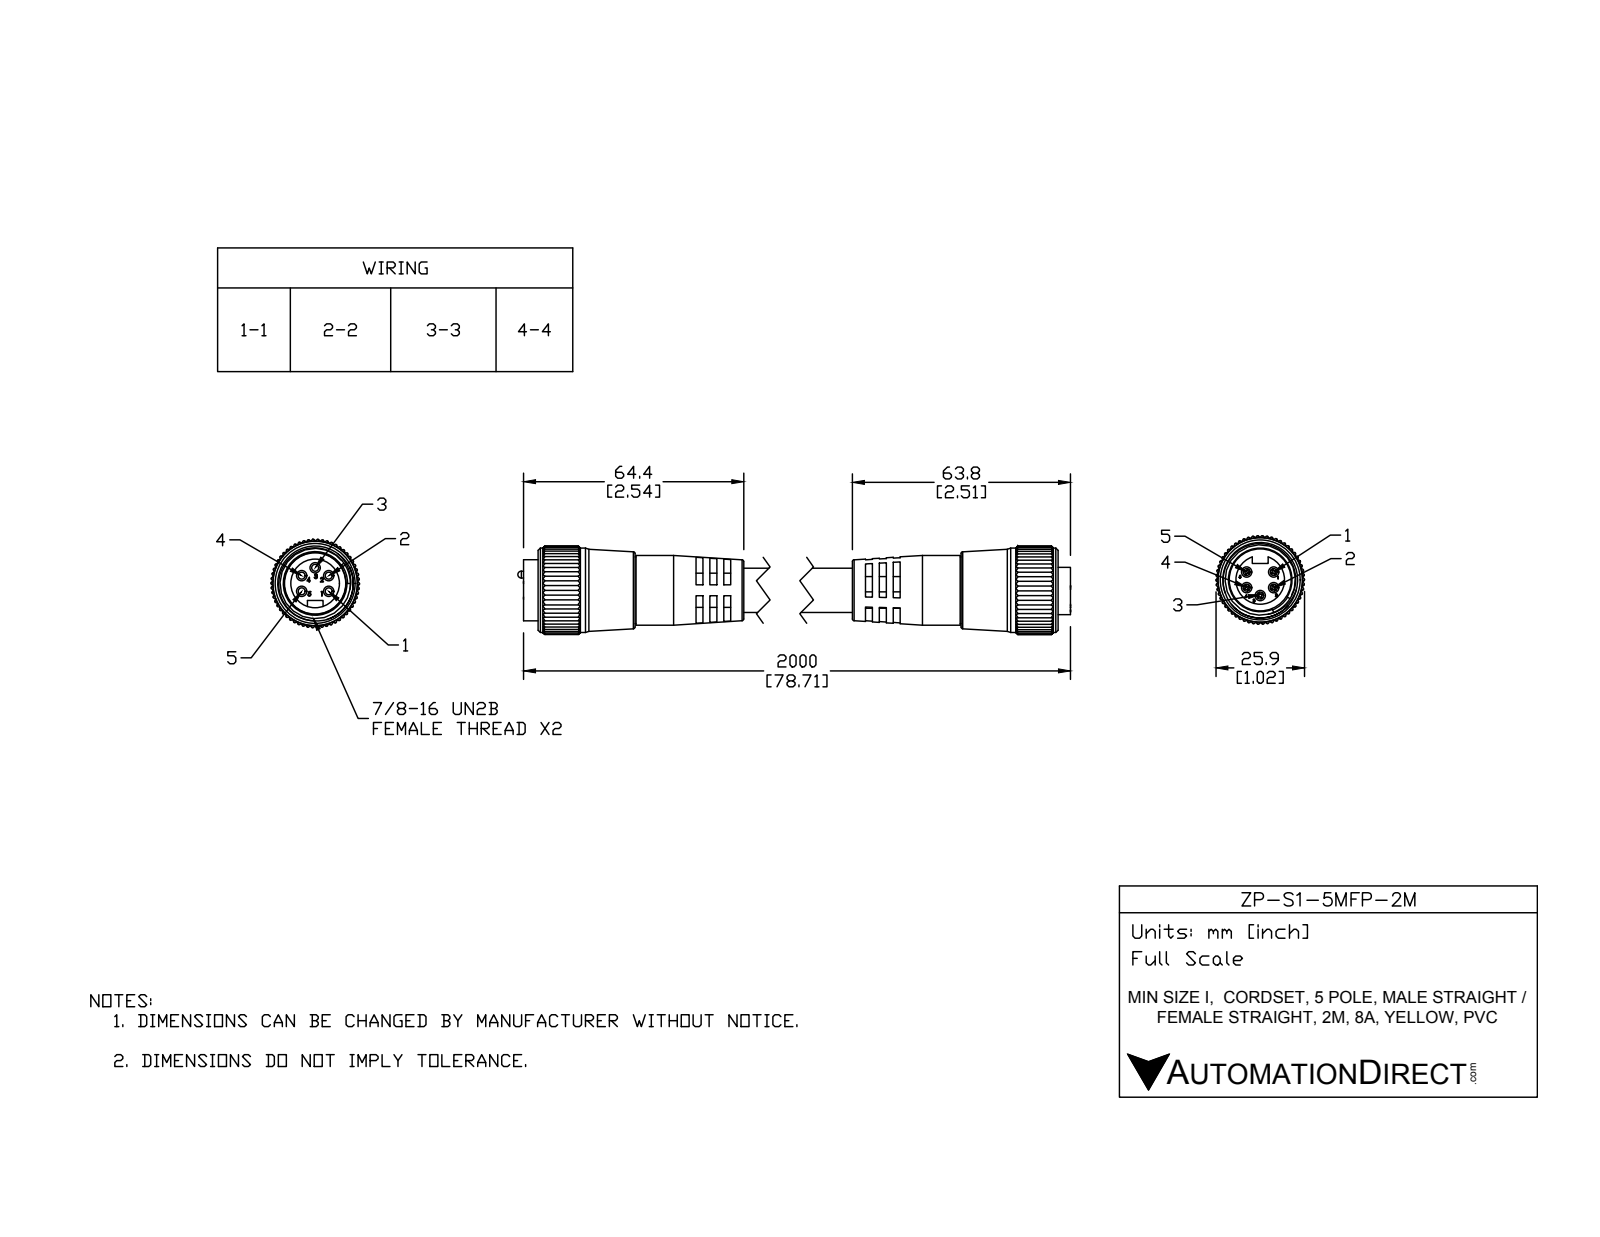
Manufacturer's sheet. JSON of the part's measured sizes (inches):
{"part_name": "ZP-S1-5MFP-2M", "step_written_by": "SolidWorks 2015 (AUTOMOTIVE_DESIGN)", "units": "inches", "bodies": {"solids": 9, "faces": 1185, "planar": 439, "cylindrical": 630, "other": 116}, "overall_size": [9.042, 1.017, 1.017], "volume_in3": 3.103, "surface_area_in2": 36.34, "round_holes": [[0.12, 5], [0.786, 1], [0.805, 1], [0.827, 1]], "round_bosses_or_shafts": [[0.079, 5], [0.972, 1], [0.803, 1], [0.768, 1], [0.704, 1], [0.56, 1], [0.39, 1], [0.12, 1]], "partial_cylinders_radius": [[0.01, 165], [0.09, 1], [0.207, 1], [0.509, 1]], "face_to_face_distances": [0.079, 0.158, 4.633, 4.474, 0.159, 4.95, 2.356, 0.159, 4.791, 4.792], "hole_center_spacings": [0.18, 0.18, 0.311, 0.312, 0.36]}
